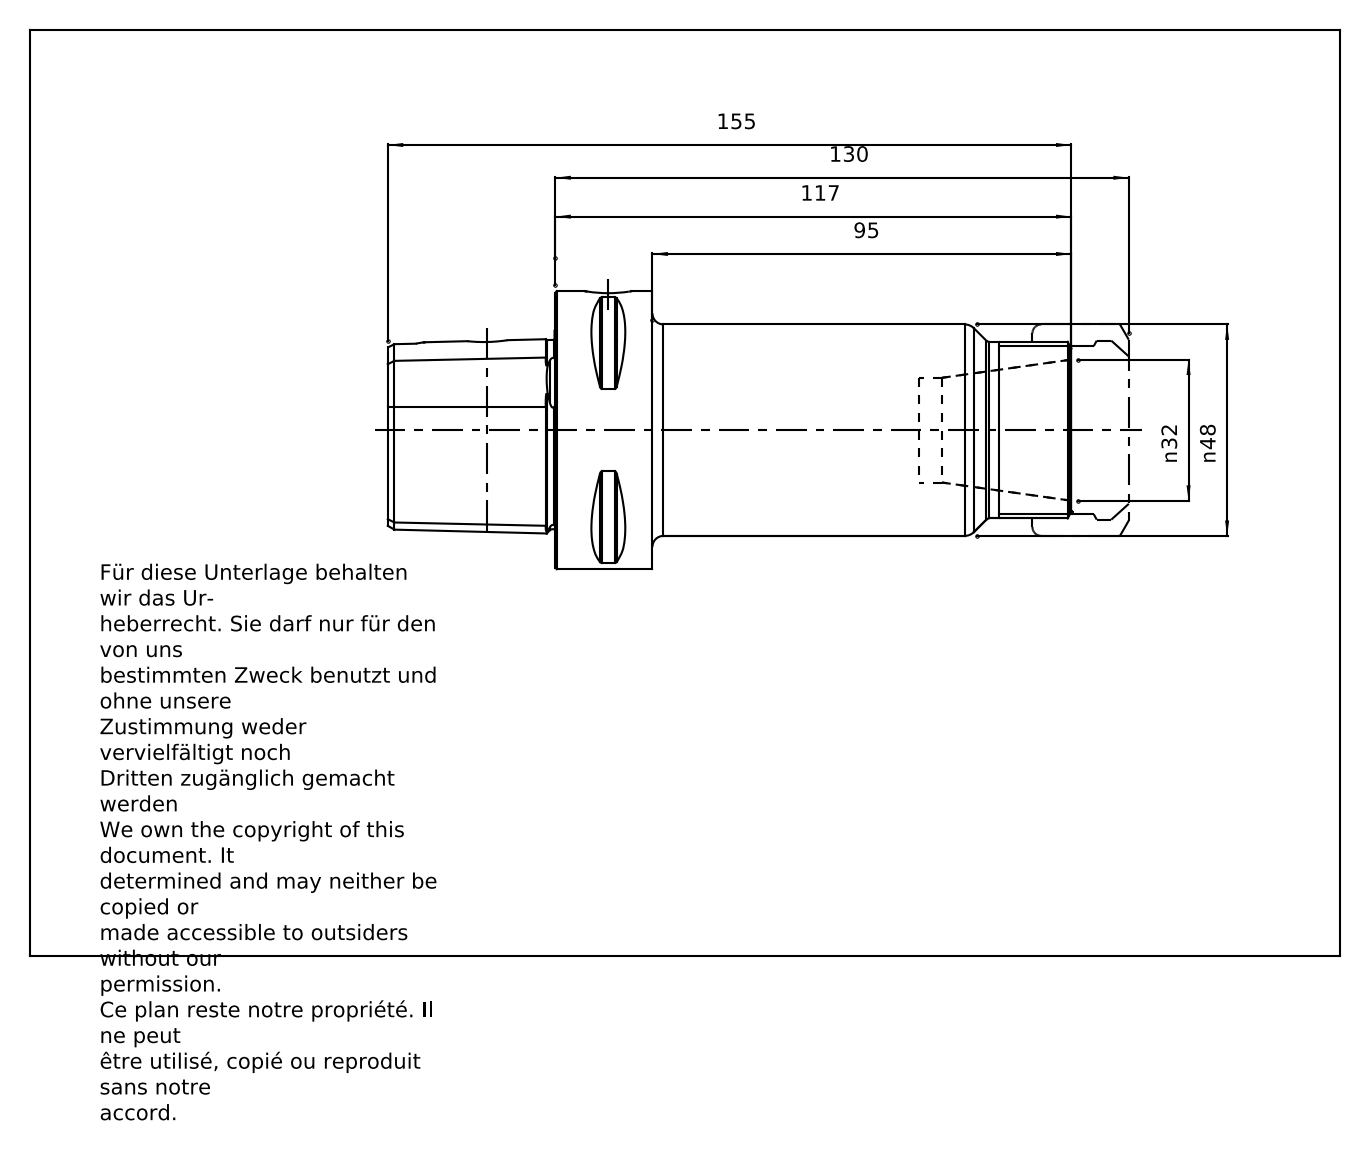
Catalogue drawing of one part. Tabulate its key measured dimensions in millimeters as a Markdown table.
| quantity | value |
| --- | --- |
| part name | CC6-024-32; 83-912-32; CC6-024-32_ASM |
| STEP written by | PRO/ENGINEER BY PARAMETRIC TECHNOLOGY CORPORATION, 2010430 (CONFIG_CONTROL_DESIGN) |
| units | millimeters |
| bodies | 2 solids, 170 faces (49 planar, 43 cylindrical, 78 other) |
| overall size | 168 × 63 × 63 |
| volume | 276 687 mm³ |
| surface area | 44 464 mm² |
| round holes (diameter × count) | 4.25 × 1, 8.1 × 1, 10.04 × 1, 18 × 1, 23.5 × 1, 28.02 × 1, 32 × 1 |
| round bosses / shafts (diameter × count) | 63 × 1, 50 × 1, 48 × 1, 40 × 1, 20 × 1 |
| partial cylindrical surfaces (radius × count) | 0.5 × 8, 2.7 × 6, 6 × 1 |
| main face-to-face distances | 107.5, 130, 22.5, 108, 22, 85.5, 13, 47, 121, 117 |
| hole center spacings | 27.5 |
